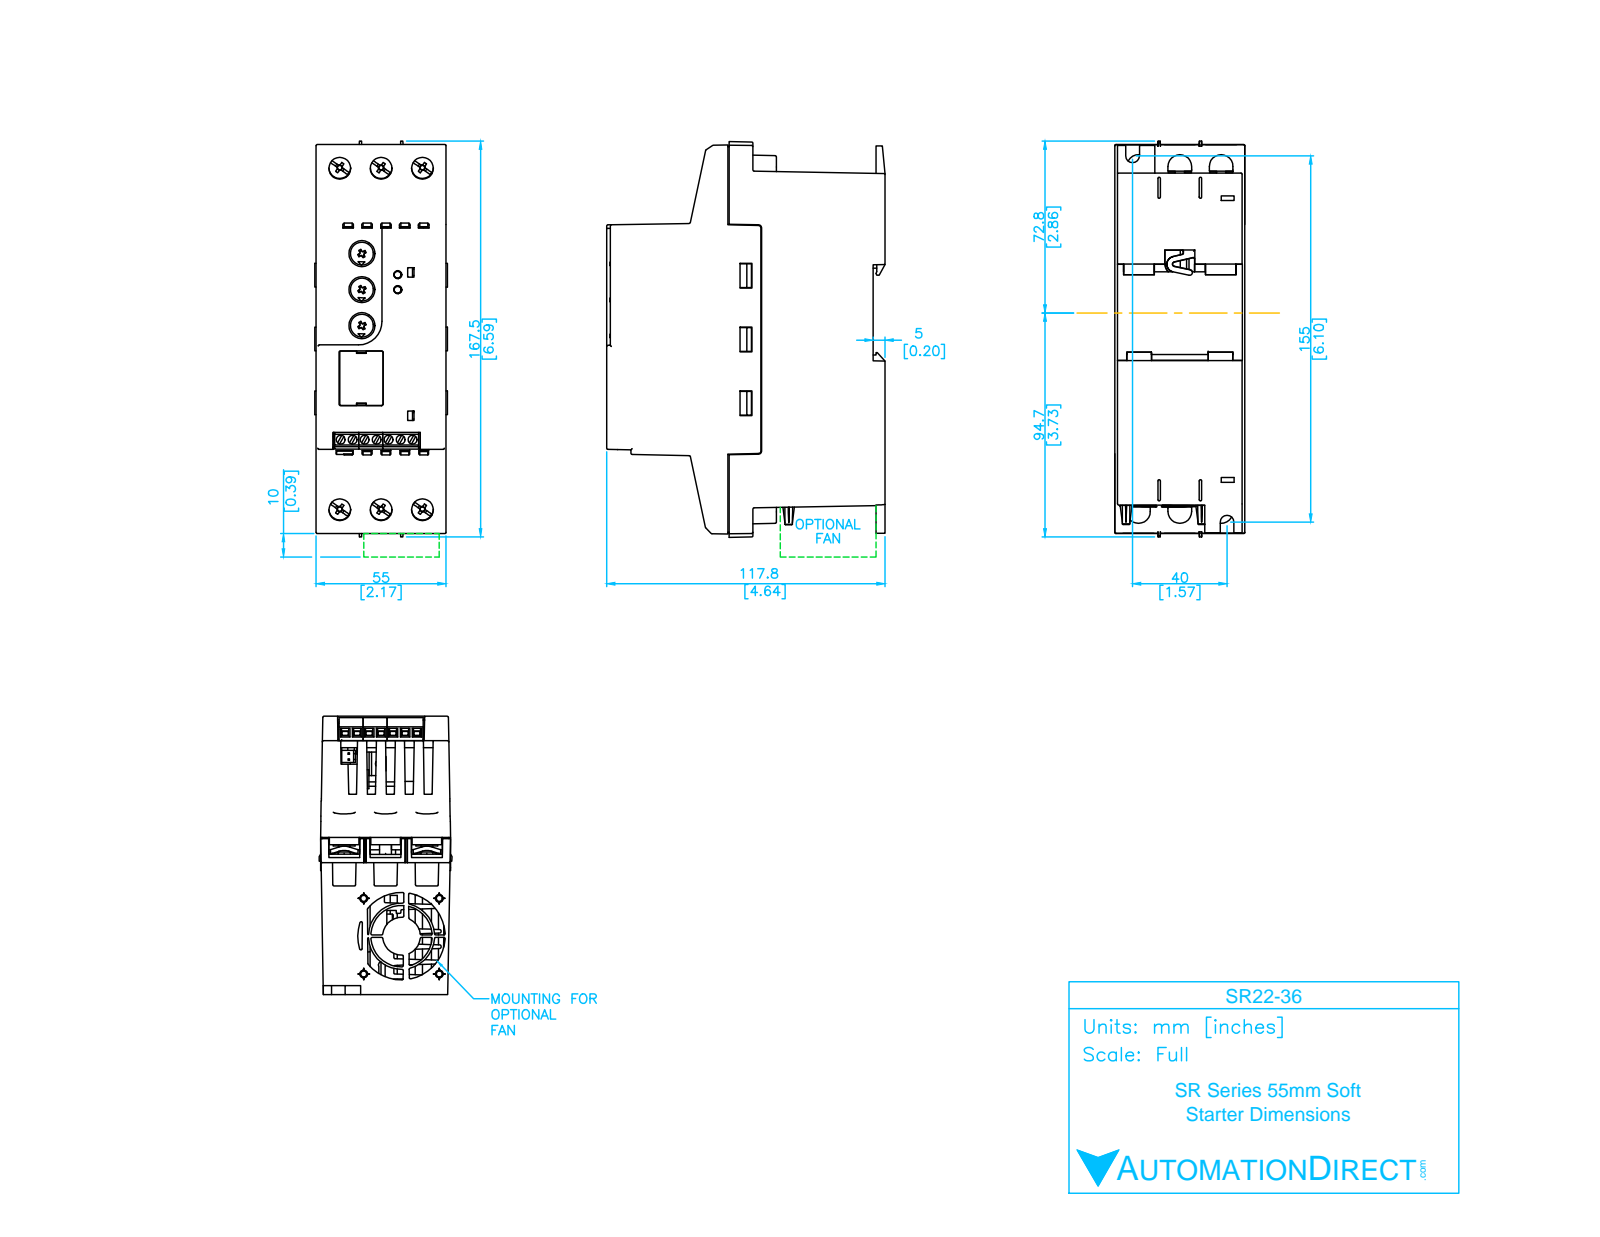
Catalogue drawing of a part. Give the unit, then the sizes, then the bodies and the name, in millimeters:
Units: millimetres
Overall size (bounding box): 164.5 × 117.8 × 55.87
Round holes (diameter × count): ⌀3.5 ×7, ⌀9.5 ×6, ⌀11.3 ×3, ⌀4 ×2, ⌀27.66 ×1, ⌀40.29 ×1
Round bosses / shafts (diameter × count): ⌀10.44 ×3, ⌀29.09 ×1, ⌀16 ×1
Partial cylindrical surfaces — rounded edges, fillets, slot ends (radius × count): R0.5 ×35, R4.88 ×6, R1 ×2, R2.75 ×2, R10 ×1
Main face-to-face distances: 54.97, 54.94, 55, 117.8, 5.14, 112.66, 141.5, 18, 0.5, 1.5
Hole centre spacings: 5.25, 10.5, 15.75, 18, 137.19, 21, 136, 15
Volume: 813 460 mm³ · Surface area: 69 575 mm²
Bodies: 1 solid, 623 faces (483 planar, 110 cylindrical, 30 other)
Part name (STEP PRODUCT): SR22-36
STEP written by: SolidWorks 2013 (AUTOMOTIVE_DESIGN)
